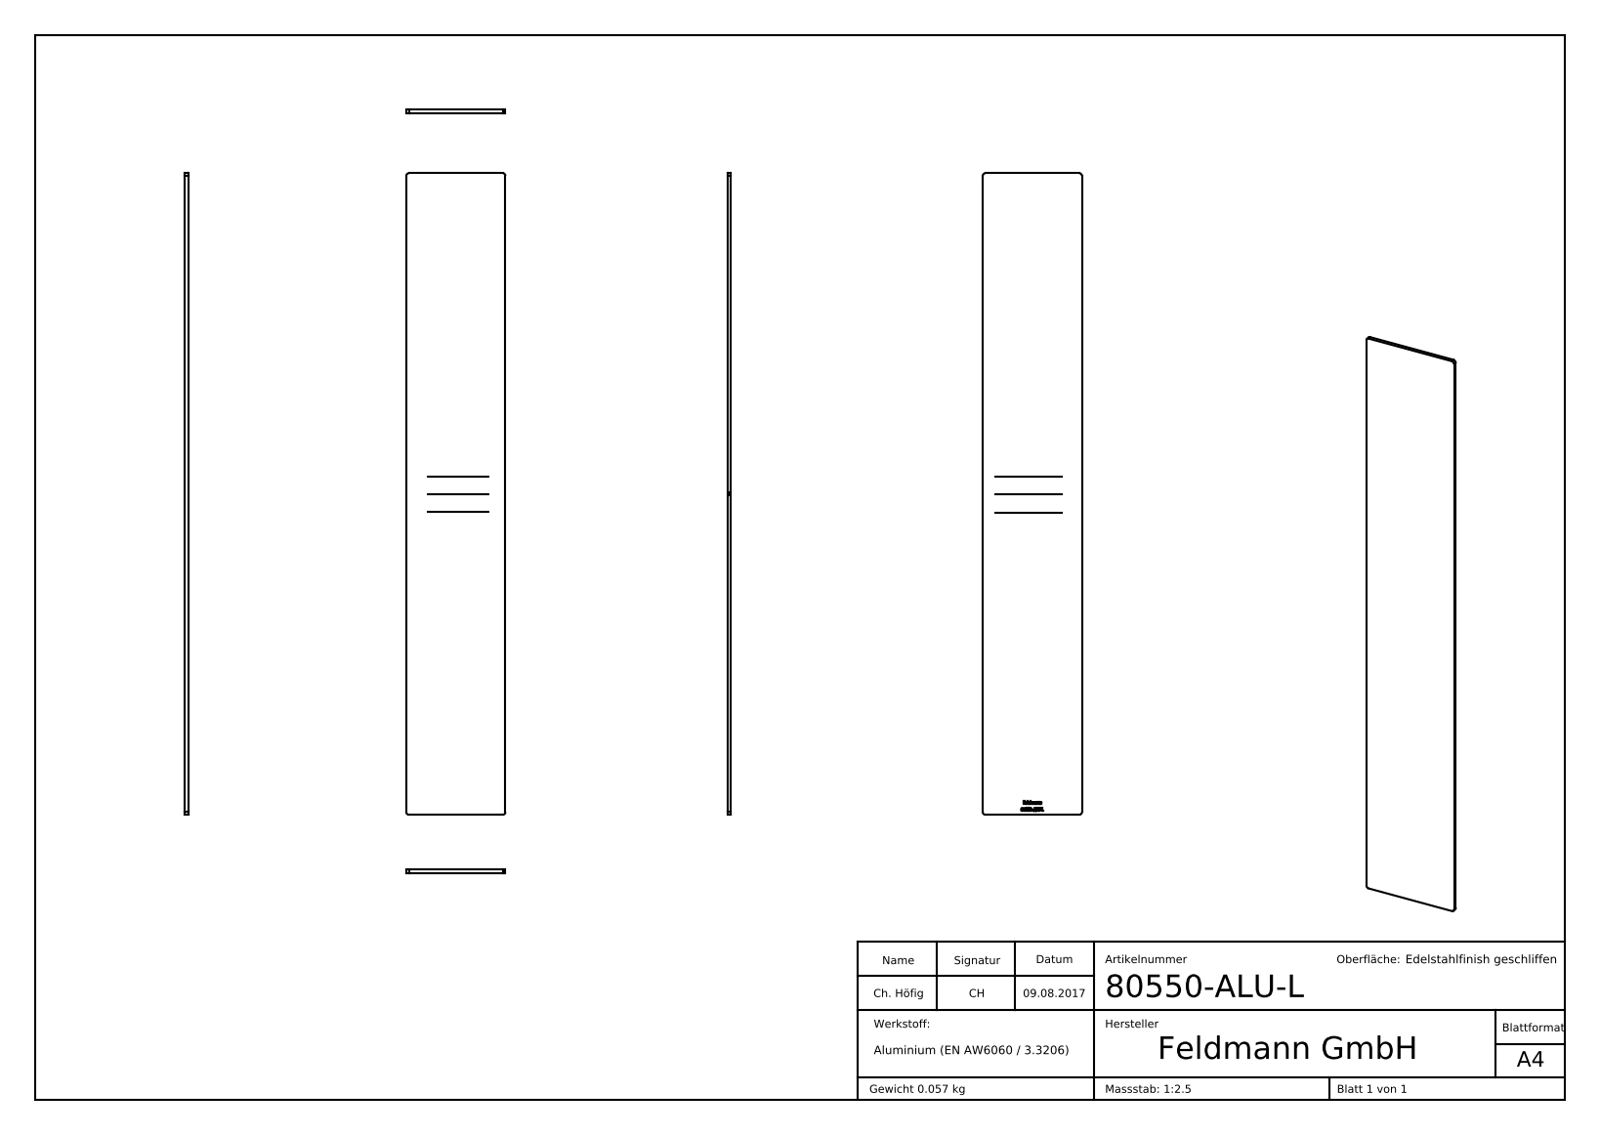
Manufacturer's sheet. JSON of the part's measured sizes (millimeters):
{"part_name": "80550-ALU-L", "step_written_by": "SolidWorks 2015 (CONFIG_CONTROL_DESIGN)", "units": "millimeters", "bodies": {"solids": 1, "faces": 246, "planar": 136, "cylindrical": 4, "other": 106}, "overall_size": [301, 46.5, 1.5], "volume_mm3": 20992, "surface_area_mm2": 29040, "partial_cylinders_radius": [[1.2, 4]], "face_to_face_distances": [1.5, 46.5, 301, 1.4, 1.19, 5.62, 2.98, 4.23, 2.64, 8.89]}
